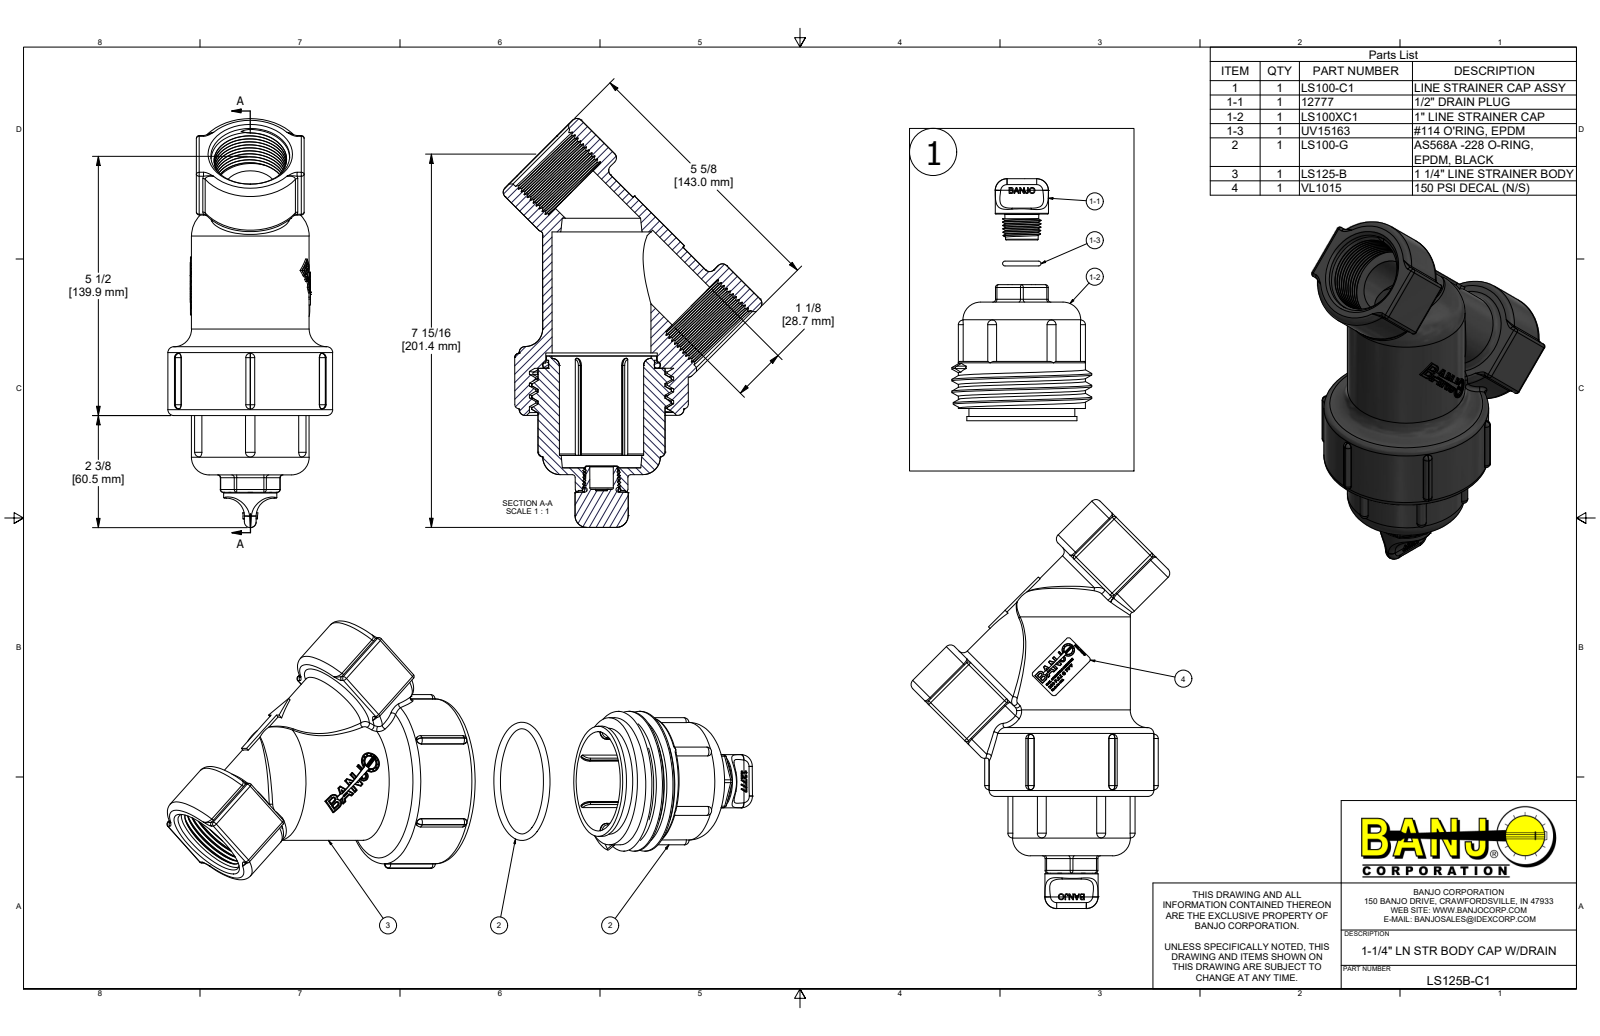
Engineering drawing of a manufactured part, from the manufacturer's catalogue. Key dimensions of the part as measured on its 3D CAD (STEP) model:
Part name (STEP PRODUCT): LS125B-C1; LS125-B; LS100-C1; LS100XC1 (+4 more)
STEP written by: Autodesk Inventor 2019 (AUTOMOTIVE_DESIGN)
Units: inches
Bodies: 6 solids, 2054 faces (1077 planar, 297 cylindrical, 680 other)
Overall size (bounding box): 34.216 × 34.216 × 3.5
Volume: 22.77 in³ · Surface area: 1 298 in²
Round holes (diameter × count): ⌀1.13 ×2, ⌀0.181 ×1, ⌀0.257 ×1, ⌀0.272 ×1, ⌀0.385 ×1, ⌀0.5 ×1, ⌀1.005 ×1, ⌀2.1 ×1, ⌀2.11 ×1, ⌀2.371 ×1, ⌀2.48 ×1, ⌀2.79 ×1
Round bosses / shafts (diameter × count): ⌀3.5 ×1, ⌀2.971 ×1, ⌀2.7 ×1, ⌀2.5 ×1, ⌀2.34 ×1, ⌀2.25 ×1, ⌀1.13 ×1, ⌀0.405 ×1
Partial cylindrical surfaces — rounded edges, fillets, slot ends (radius × count): R0.06 ×54, R0.09 ×35, R0.03 ×18, R0.1 ×7, R0.15 ×6, R0.026 ×2, R0.033 ×2, R0.039 ×2
Main face-to-face distances: 2.29, 2.115, 1.06, 4.569, 1.26, 0.07, 2.895, 5.01, 2.57, 0.145
Hole centre spacings: 0.919
